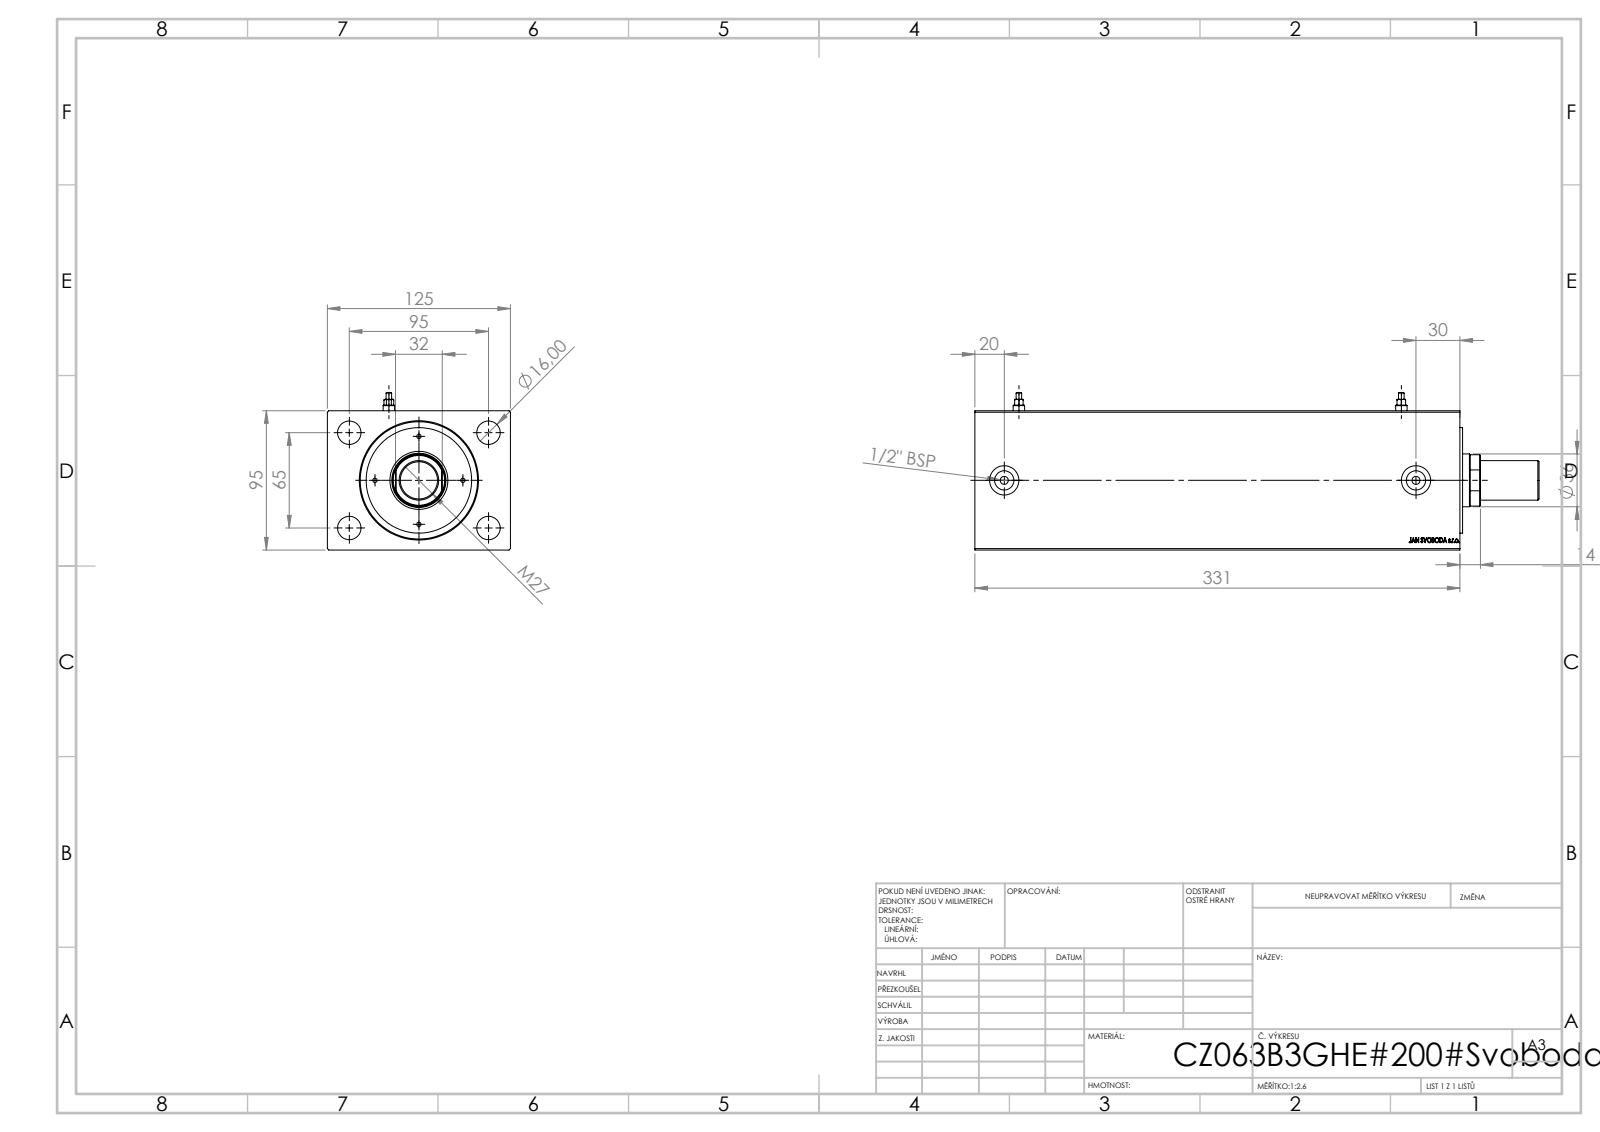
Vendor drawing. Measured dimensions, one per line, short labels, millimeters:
name: V500CZ; V500CZ_B_VC; V500CZ_SMALL_MALE_METRIC; Zatka_Cushioning3
written by: SolidWorks 2019 (CONFIG_CONTROL_DESIGN)
unit: mm
bodies: 6 solids, 940 faces (426 planar, 76 cylindrical, 438 other)
size: 385 × 125 × 107.5
volume: 3 475 000 mm³; area: 315 030 mm²
holes: 4× ⌀3, 4× ⌀16, 2× ⌀1.8, 2× ⌀5.5, 2× ⌀8, 2× ⌀13.16, 2× ⌀20, 1× ⌀25.5, 1× ⌀36, 1× ⌀37, 1× ⌀63, 1× ⌀80
bosses: 2× ⌀7.8, 2× ⌀3.8, 1× ⌀72, 1× ⌀27
rounds: 1× R17.5
face distances: 95, 125, 331, 310.2, 20.8, 14, 12.2, 1.8, 298, 318.8
hole spacings: 30, 36.91, 42.43, 47.57, 57.55, 78.5, 84.04, 60
